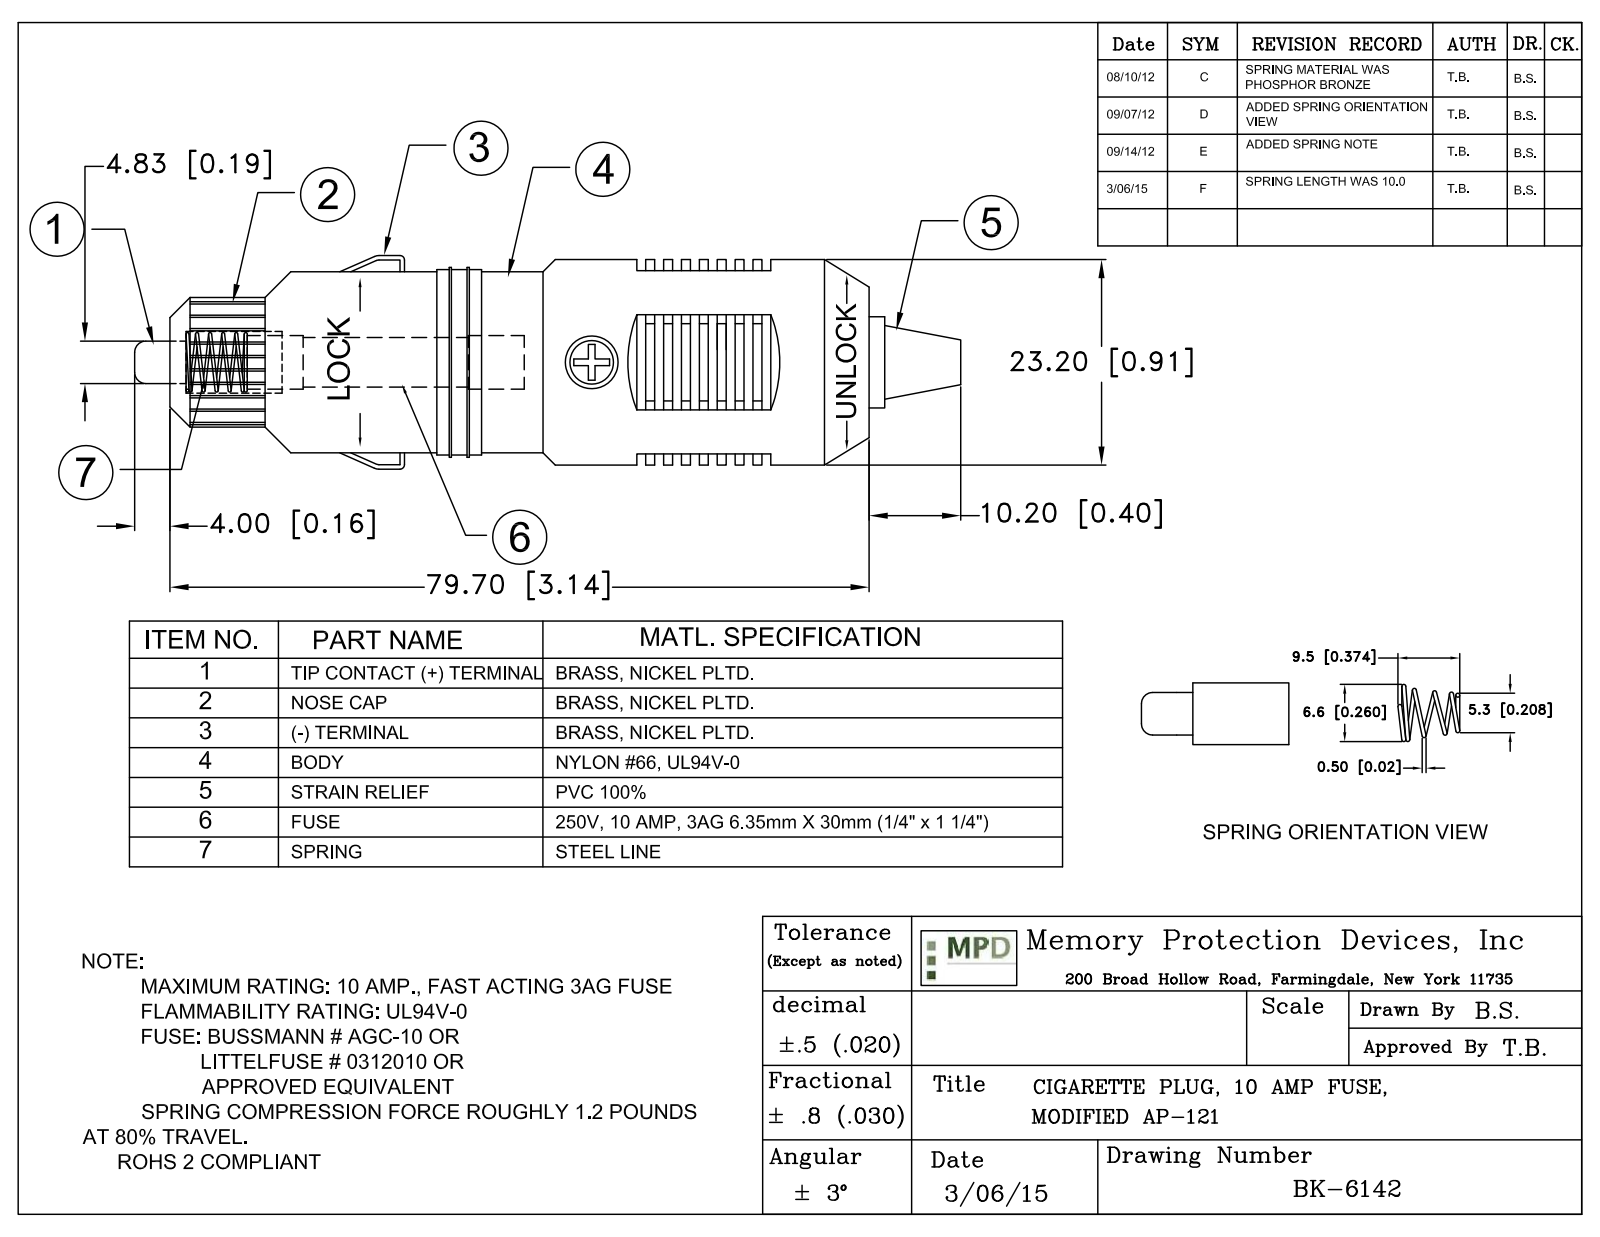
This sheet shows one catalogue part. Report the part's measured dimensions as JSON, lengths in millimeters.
{"part_name": "BK-6142", "step_written_by": "SolidWorks 2017 (AUTOMOTIVE_DESIGN)", "units": "millimeters", "bodies": {"solids": 5, "faces": 172, "planar": 128, "cylindrical": 28, "other": 16}, "overall_size": [93.9, 23.2, 23.2], "volume_mm3": 27696, "surface_area_mm2": 7153, "round_bosses_or_shafts": [[23.2, 1], [21.35, 1], [20.86, 1], [14.96, 1], [10, 1], [4.83, 1]], "partial_cylinders_radius": [[13, 4]], "face_to_face_distances": [68.7, 2.02, 4.03, 6.05, 1.1, 20.8, 2.01, 3.12, 5.13, 7.15]}
